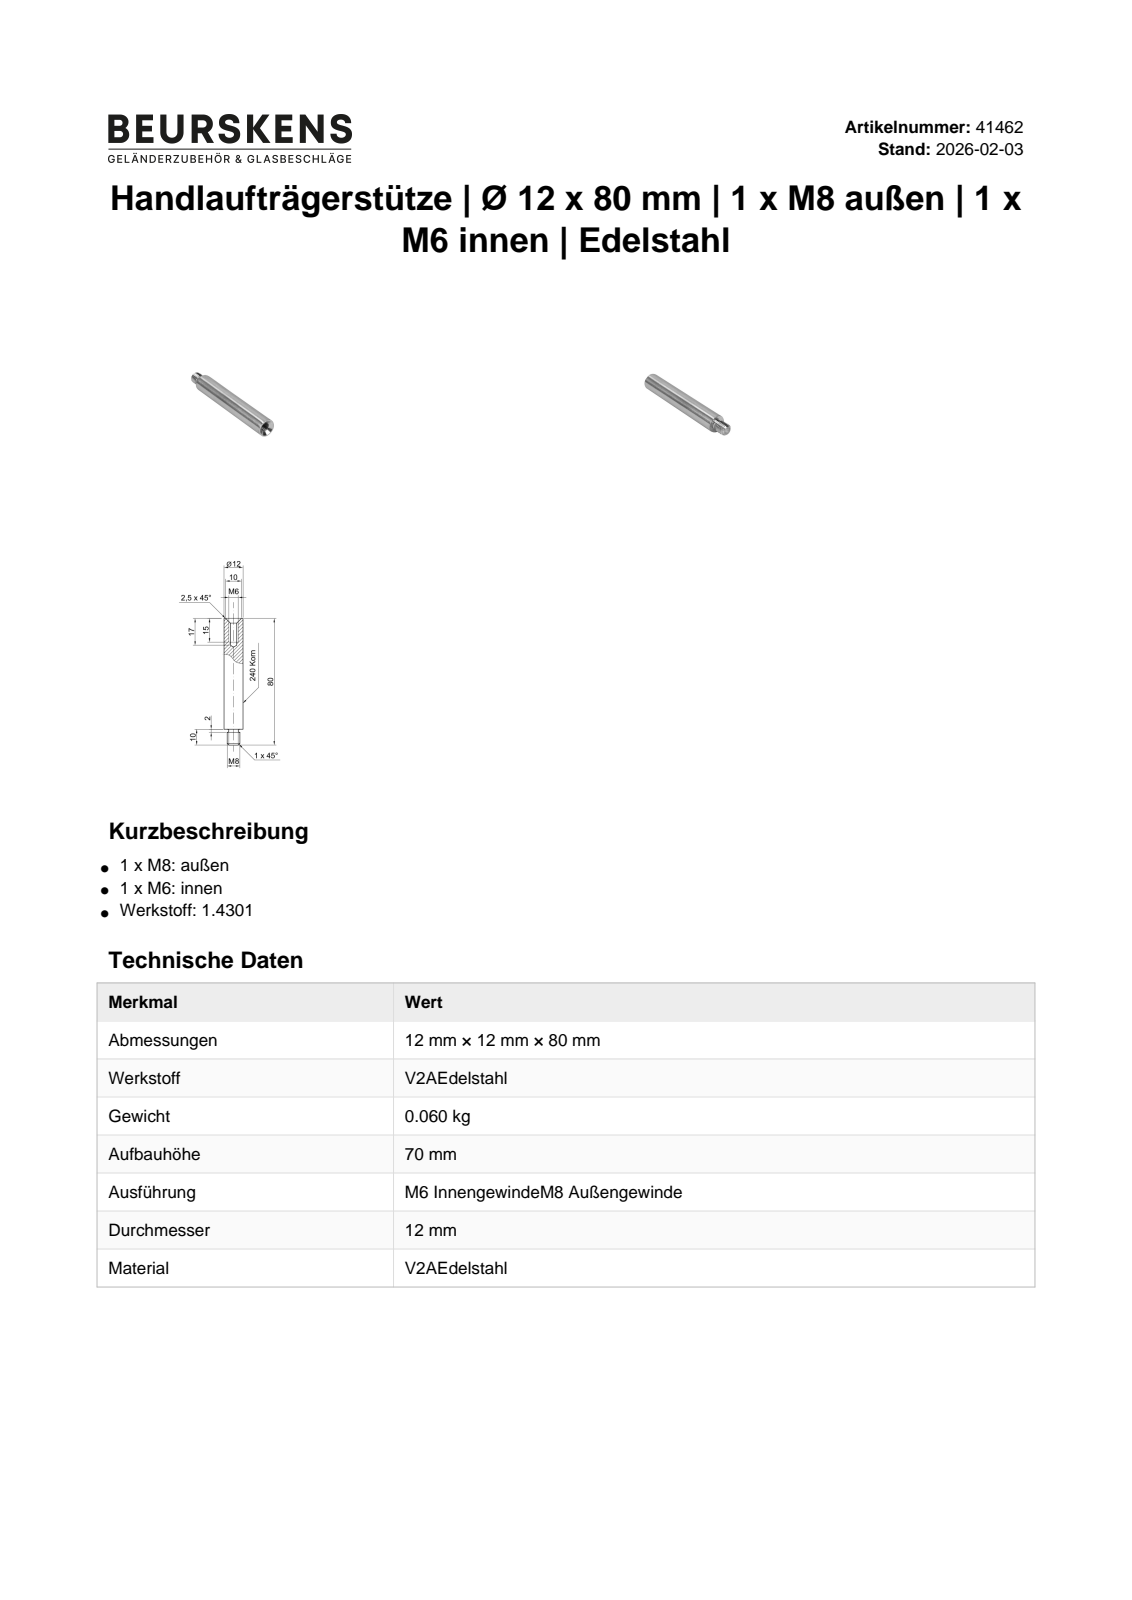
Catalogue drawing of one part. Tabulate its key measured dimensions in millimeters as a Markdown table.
| quantity | value |
| --- | --- |
| part name | 41462 |
| STEP written by | Autodesk Inventor 2022 (AUTOMOTIVE_DESIGN) |
| units | millimeters |
| bodies | 1 solid, 11 faces (5 planar, 4 cylindrical, 2 other) |
| overall size | 80 × 12 × 12 |
| volume | 7 817 mm³ |
| surface area | 3 441 mm² |
| round holes (diameter × count) | 6 × 1 |
| round bosses / shafts (diameter × count) | 12 × 1, 8 × 1 |
| main face-to-face distances | 10, 53, 63, 55, 2, 8, 17, 70, 72, 80 |
